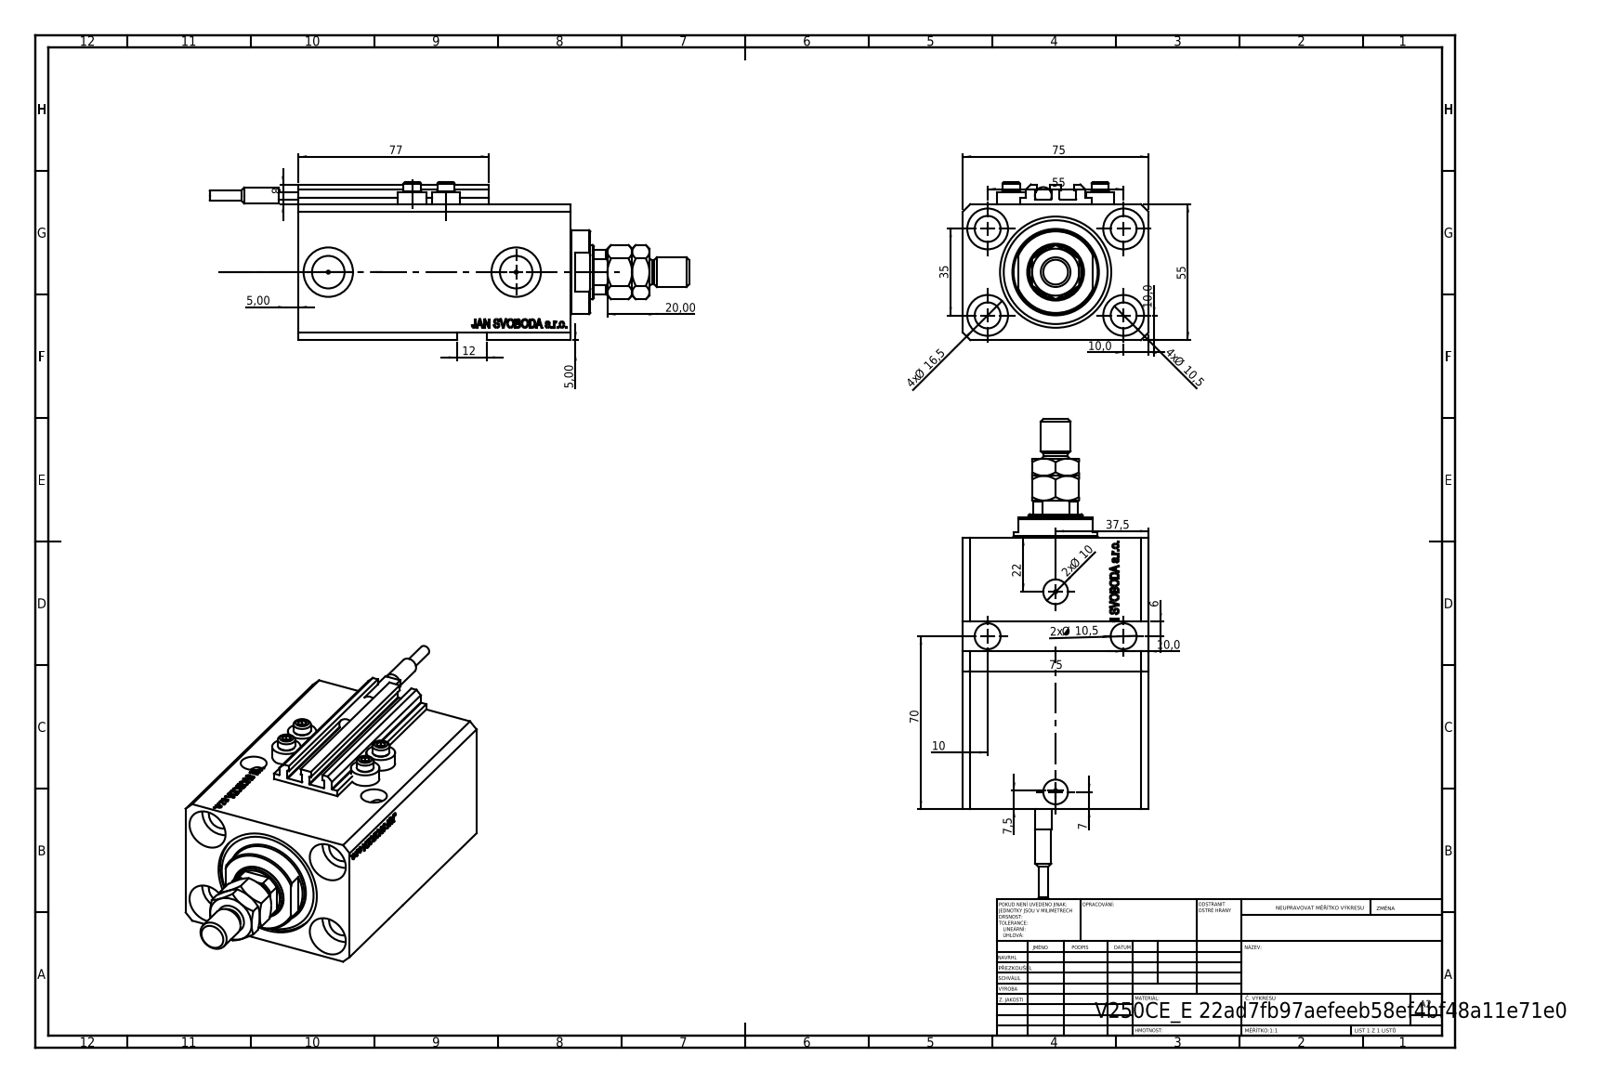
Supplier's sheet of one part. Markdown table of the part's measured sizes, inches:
| quantity | value |
| --- | --- |
| part name | SWITCH_V250CE; MTA; ALLEN BOLT V250CE; V250CE_E_Body (+2 more) |
| STEP written by | SolidWorks 2019 (CONFIG_CONTROL_DESIGN) |
| units | inches |
| bodies | 10 solids, 1139 faces (545 planar, 136 cylindrical, 458 other) |
| overall size | 7.634 × 2.953 × 2.52 |
| volume | 24.2 in³ |
| surface area | 155.7 in² |
| round holes (diameter × count) | 0.413 × 7, 0.049 × 4, 0.157 × 4, 0.65 × 4, 0.394 × 2, 0.518 × 2, 0.787 × 2, 0.866 × 1, 1.26 × 1, 1.772 × 1 |
| round bosses / shafts (diameter × count) | 0.457 × 4, 0.276 × 4, 1.339 × 1, 0.472 × 1, 0.394 × 1, 0.268 × 1, 0.256 × 1, 0.157 × 1 |
| partial cylindrical surfaces (radius × count) | 0.008 × 10, 0.413 × 1 |
| main face-to-face distances | 2.165, 2.953, 0.118, 4.331, 3.264, 1.067, 0.39, 2.244, 2.874, 3.941 |
| hole center spacings | 1.283, 2.165, 0.535, 0.555, 1.016, 1.294, 1.324, 1.378 |
